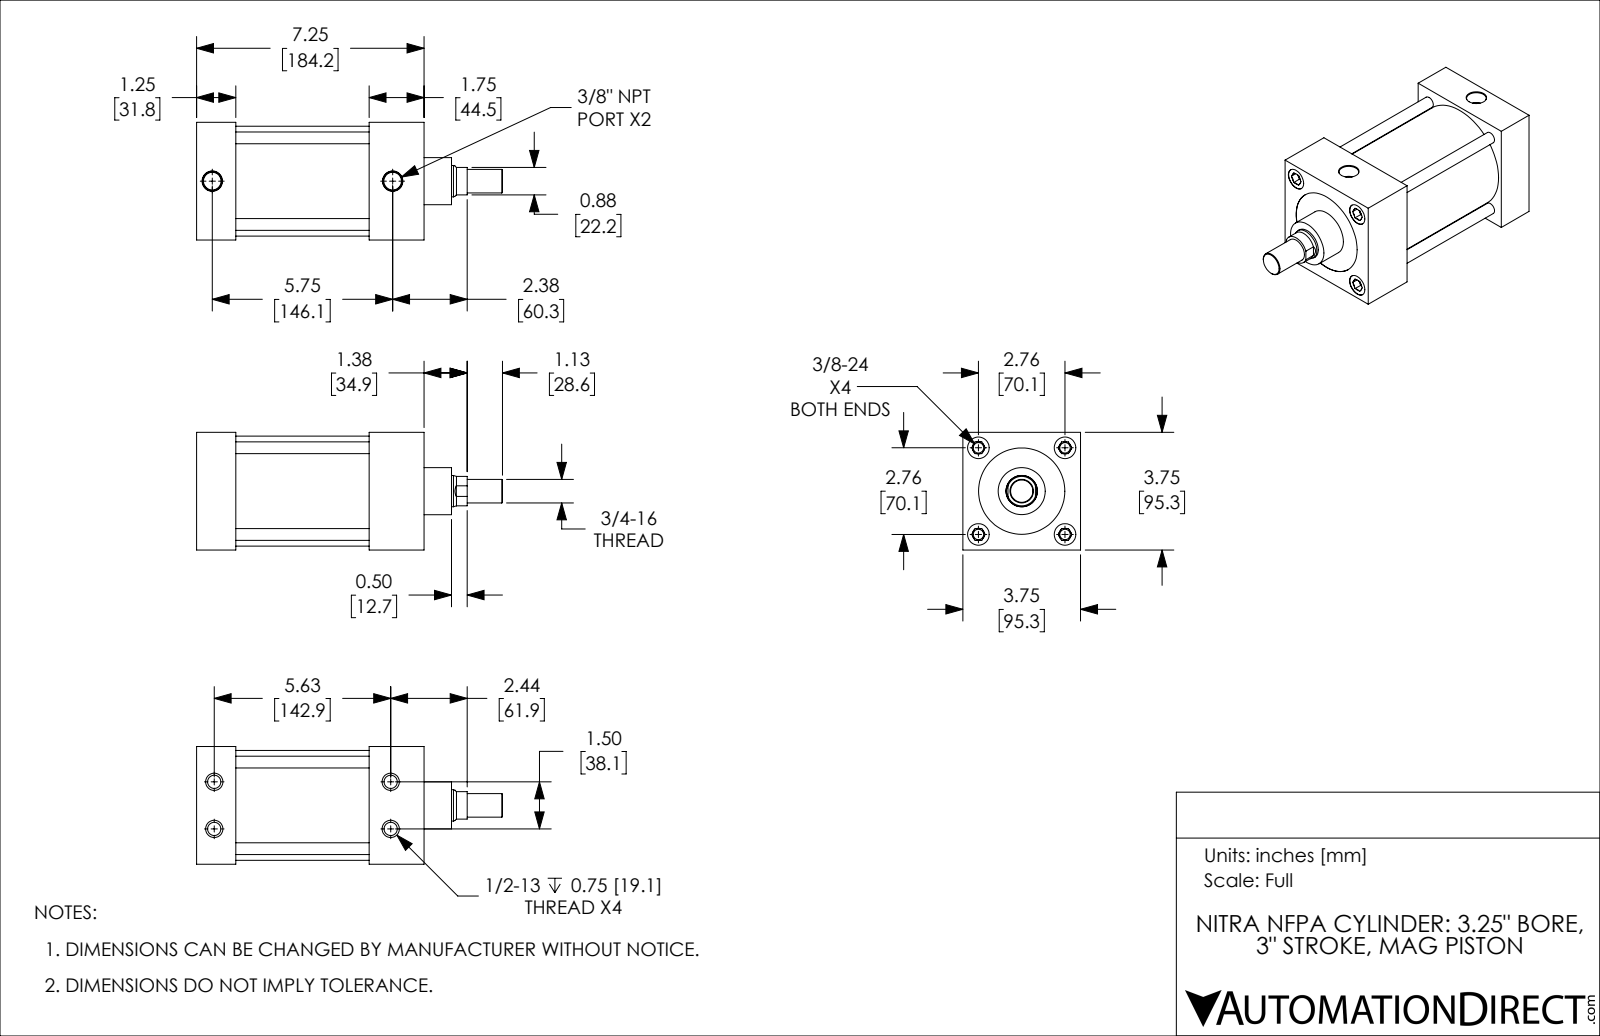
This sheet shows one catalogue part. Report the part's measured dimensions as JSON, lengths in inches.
{"part_name": "D252030DT-M_PISTON_KK1; D252030DT-M_BODY; D252030DT-M", "step_written_by": "SolidWorks 2019 (CONFIG_CONTROL_DESIGN)", "units": "inches", "bodies": {"solids": 2, "faces": 198, "planar": 58, "cylindrical": 62, "other": 78}, "overall_size": [9.75, 3.75, 3.75], "volume_in3": 62.6, "surface_area_in2": 288.6, "round_holes": [[0.332, 4], [0.422, 4], [0.687, 4], [0.562, 2], [1, 1], [2.75, 1], [3.251, 1]], "round_bosses_or_shafts": [[0.375, 4], [3.501, 1], [3.249, 1], [1.5, 1], [0.999, 1], [0.75, 1]], "partial_cylinders_radius": [[0.469, 1]], "face_to_face_distances": [1.25, 3.75, 4.25, 5.5, 2.5, 3, 7.25, 6, 4.75, 1.75], "hole_center_spacings": [0.753, 1.952, 2.76, 5.737, 1.5, 3.903, 5.625, 5.821]}
